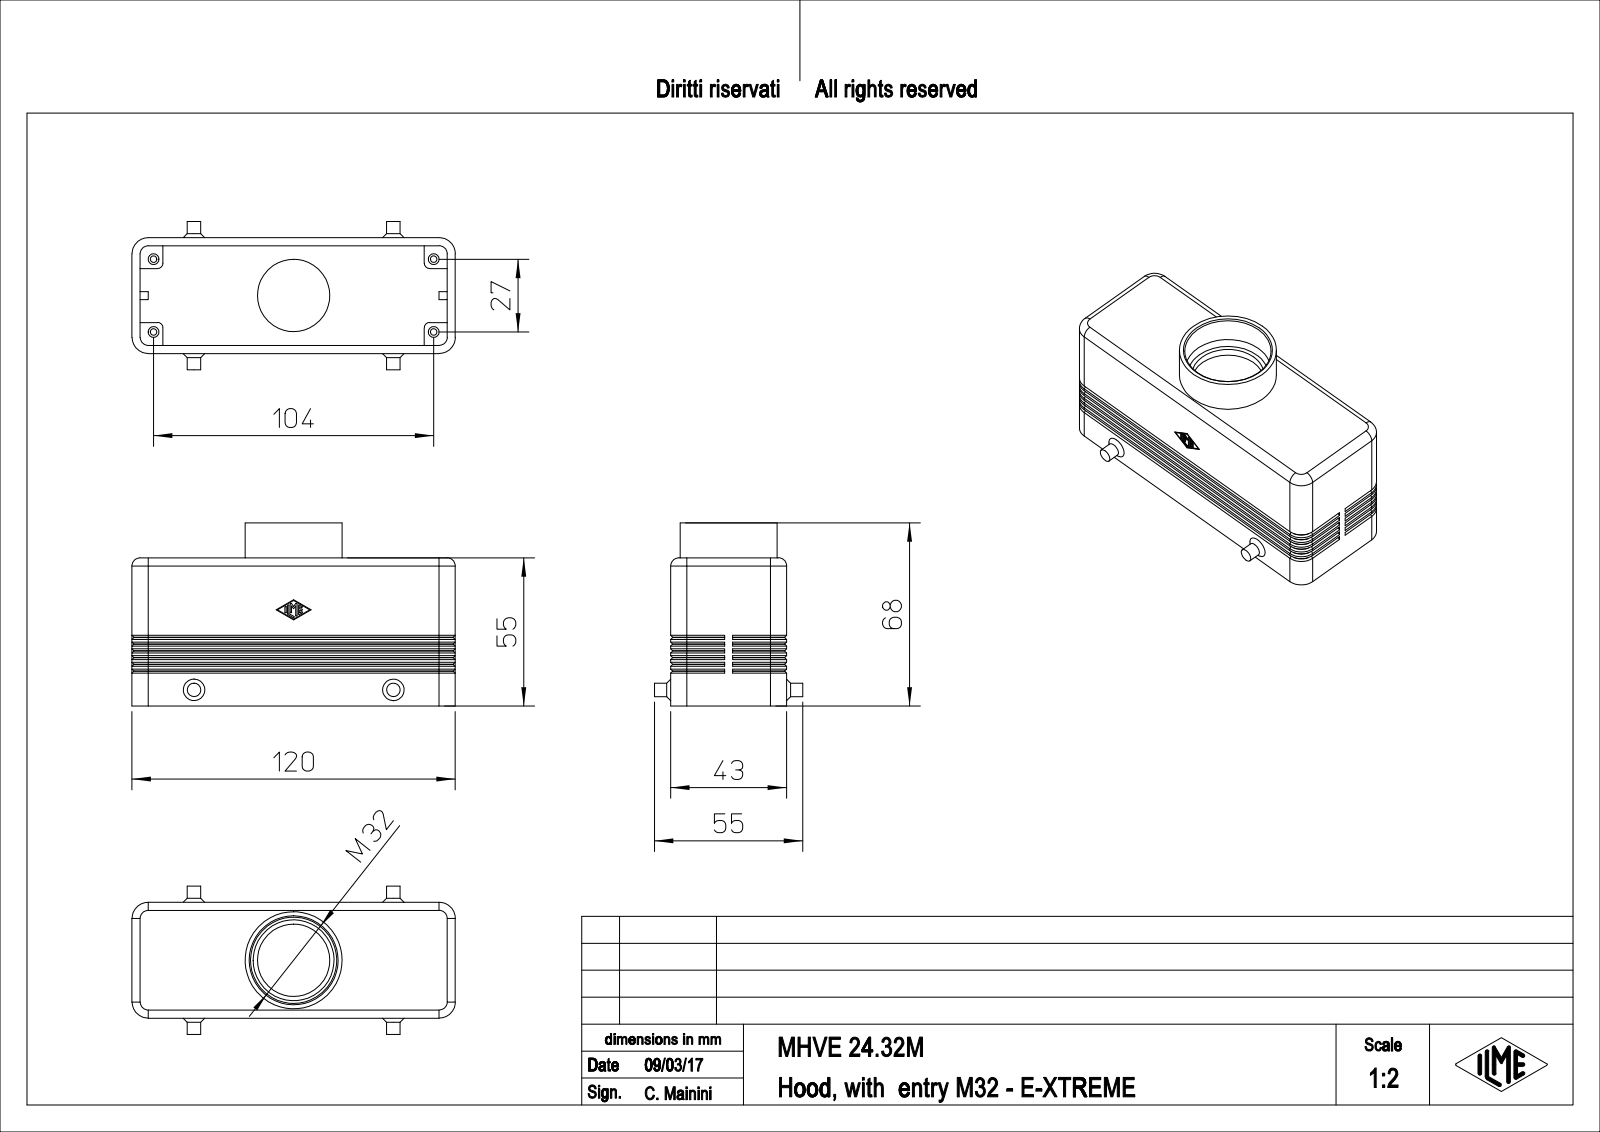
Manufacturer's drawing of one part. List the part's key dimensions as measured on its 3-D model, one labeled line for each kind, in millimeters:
Part name (STEP PRODUCT): MHVE_24.32M
STEP written by: PTC Creo Elements/Direct Modeling 19.0E 27-Jun-2016 (C) Parametric Technology GmbH (AUTOMOTIVE_DESIGN)
Units: millimetres
Bodies: 1 solid, 402 faces (220 planar, 110 cylindrical, 72 other)
Overall size (bounding box): 120 × 68 × 55
Volume: 75 578 mm³ · Surface area: 46 811 mm²
Round holes (diameter × count): ⌀2.46 ×4, ⌀4 ×4, ⌀26.84 ×1, ⌀32 ×1
Round bosses / shafts (diameter × count): ⌀5 ×2, ⌀36 ×1
Partial cylindrical surfaces — rounded edges, fillets, slot ends (radius × count): R0.25 ×14, R3 ×8, R2 ×4, R5.3 ×4, R6 ×4, R1.5 ×1
Main face-to-face distances: 3, 40, 37, 43, 11.5, 8.5, 1.77, 117, 5.3, 20
Hole centre spacings: 53.72, 27, 104, 107.45
